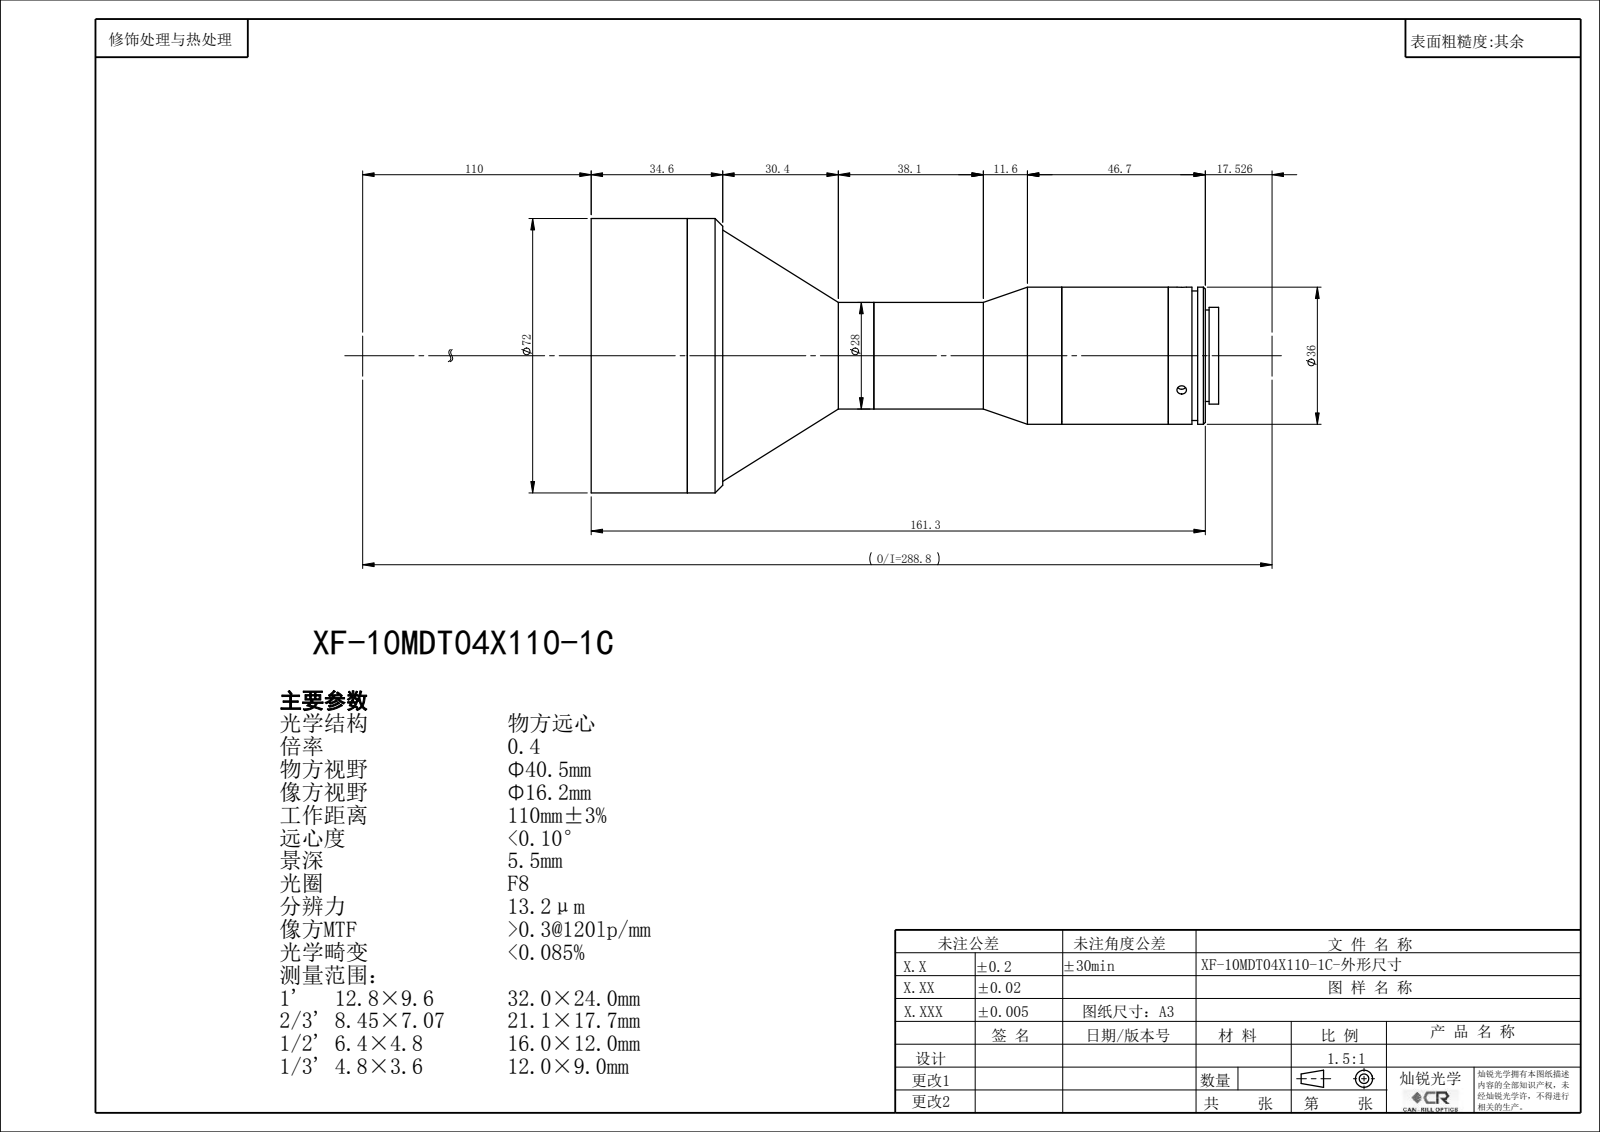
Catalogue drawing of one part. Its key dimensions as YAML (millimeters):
step_written_by: "SolidWorks 2014 (CONFIG_CONTROL_DESIGN)"
units: millimeters
bodies: {solids: 0, faces: 77, planar: 23, cylindrical: 42, other: 12}
overall_size: [164.77, 72, 72]
round_holes:
  - {diameter: 2.5, count: 3}
  - {diameter: 21.4, count: 1}
  - {diameter: 24, count: 1}
  - {diameter: 57, count: 1}
  - {diameter: 62, count: 1}
  - {diameter: 66, count: 1}
round_bosses_or_shafts:
  - {diameter: 72, count: 1}
  - {diameter: 36, count: 1}
  - {diameter: 34, count: 1}
  - {diameter: 28, count: 1}
  - {diameter: 25.4, count: 1}
face_to_face_distances: [25.25, 5.27, 19.98, 151.57, 146.3, 126.32, 161.27, 156, 136.02, 9.7]
